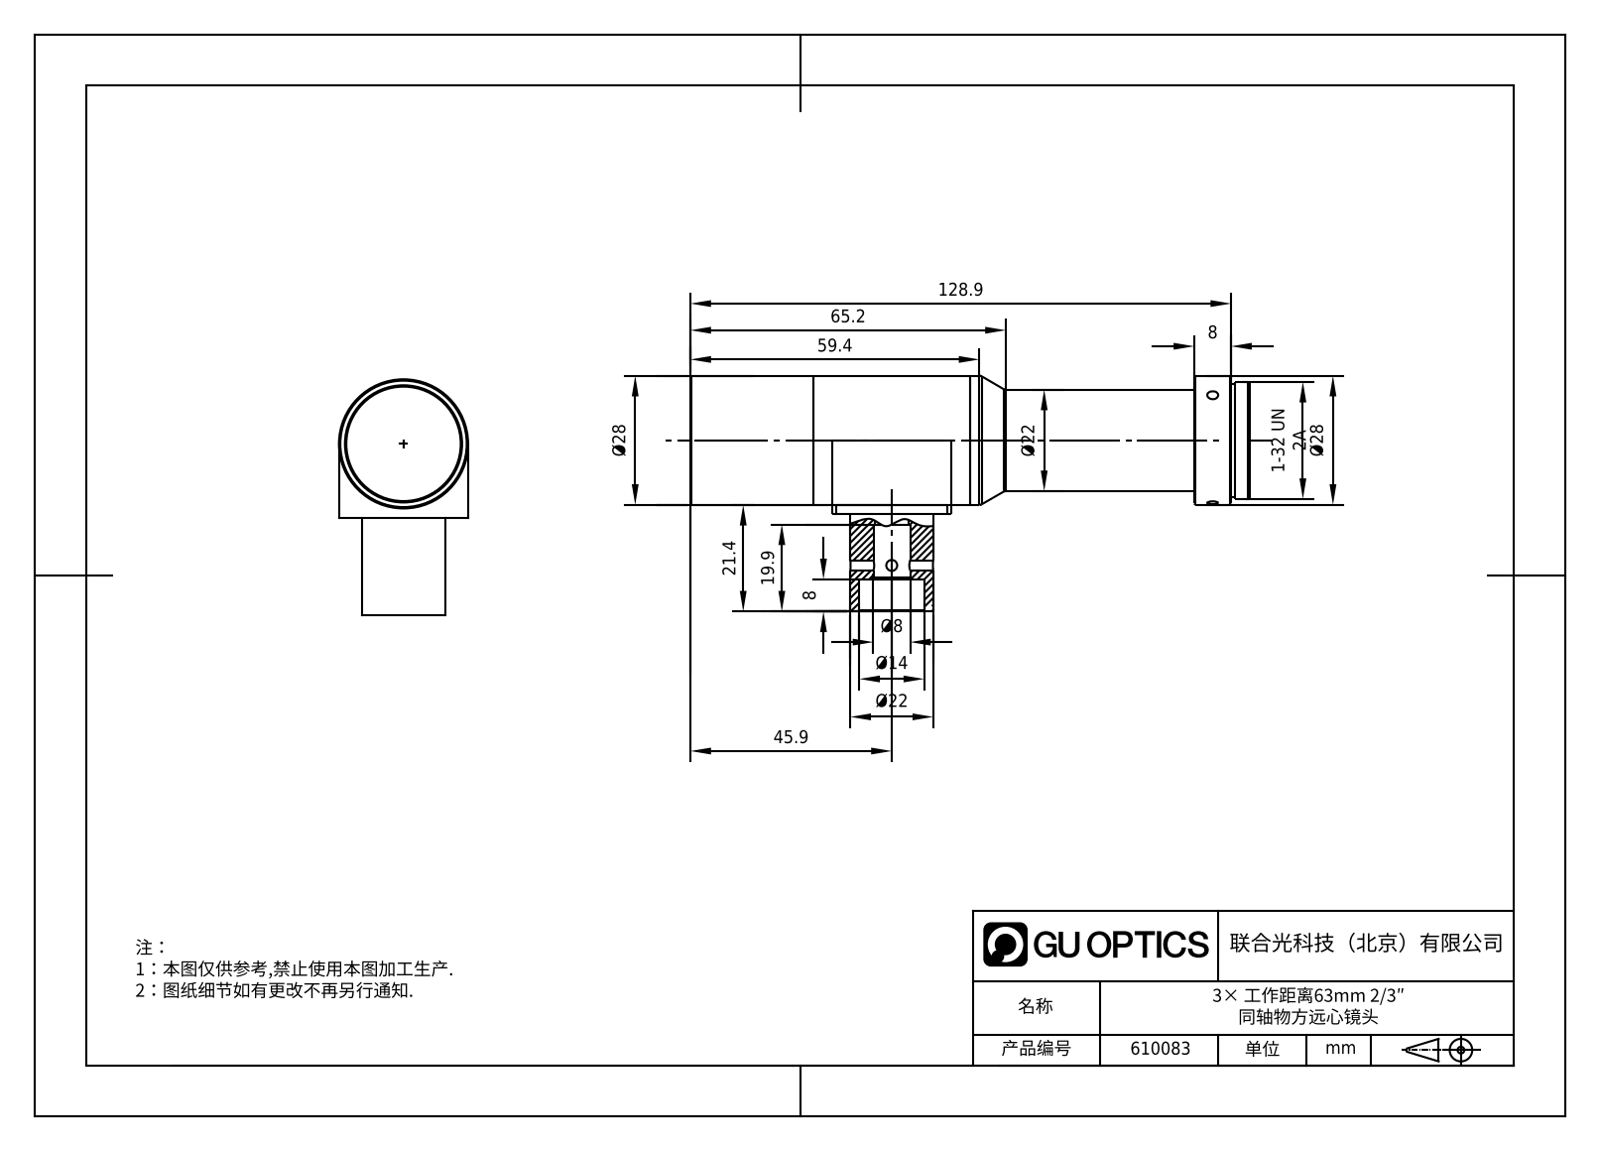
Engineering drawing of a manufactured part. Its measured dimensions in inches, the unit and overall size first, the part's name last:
Units: inches
Overall size (bounding box): 5.232 × 1.945 × 1.102
Round bosses / shafts (diameter × count): ⌀0.866 ×2, ⌀1.102 ×1, ⌀1 ×1, ⌀0.961 ×1
Main face-to-face distances: 5.232, 1.102, 0.843, 4.76, 0.472, 5.075, 0.315, 0.157, 1.295, 2.319
Volume: 4.75 in³ · Surface area: 21.78 in²
Bodies: 1 solid, 40 faces (13 planar, 13 cylindrical, 14 other)
Part name (STEP PRODUCT): WWH40-63CTV3
STEP written by: SolidWorks 2017 (CONFIG_CONTROL_DESIGN)
